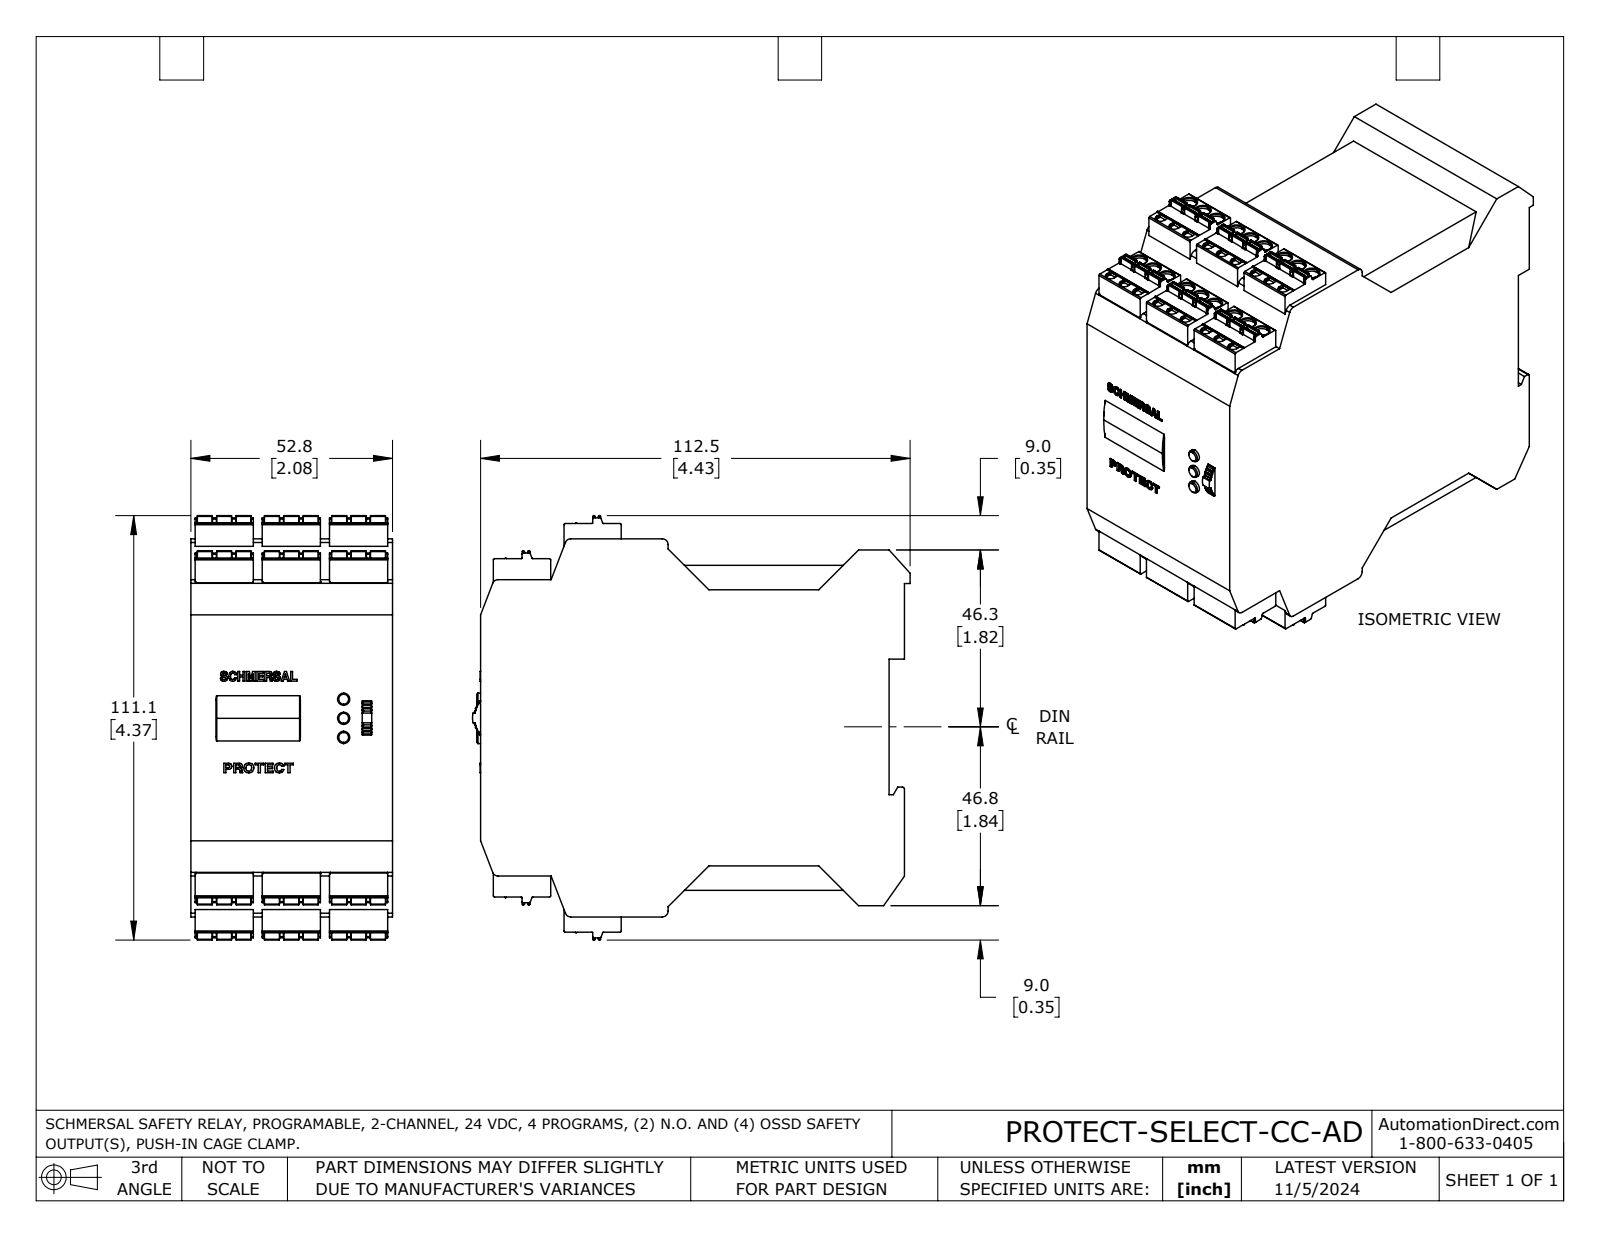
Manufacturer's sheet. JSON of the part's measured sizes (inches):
{"part_name": "PROTECT-SELECT-CC-AD", "step_written_by": "SolidWorks 2023 (AUTOMOTIVE_DESIGN)", "units": "inches", "bodies": {"solids": 1, "faces": 2122, "planar": 1152, "cylindrical": 652, "other": 318}, "overall_size": [4.512, 4.374, 2.079], "volume_in3": 31.71, "surface_area_in2": 72.38, "round_holes": [[0.157, 36]], "round_bosses_or_shafts": [[0.126, 3]], "partial_cylinders_radius": [[0.012, 35], [0.046, 33], [0.008, 22], [0.01, 8], [0.059, 6], [0.02, 1], [0.283, 1], [0.295, 1]], "face_to_face_distances": [2.079, 0.157, 4.37, 3.35, 4.213, 0.274, 3.624, 0.693, 0.728, 0.362], "hole_center_spacings": [0.728, 0.2, 0.693, 0.755, 1.005, 0.016, 0.493, 0.893]}
